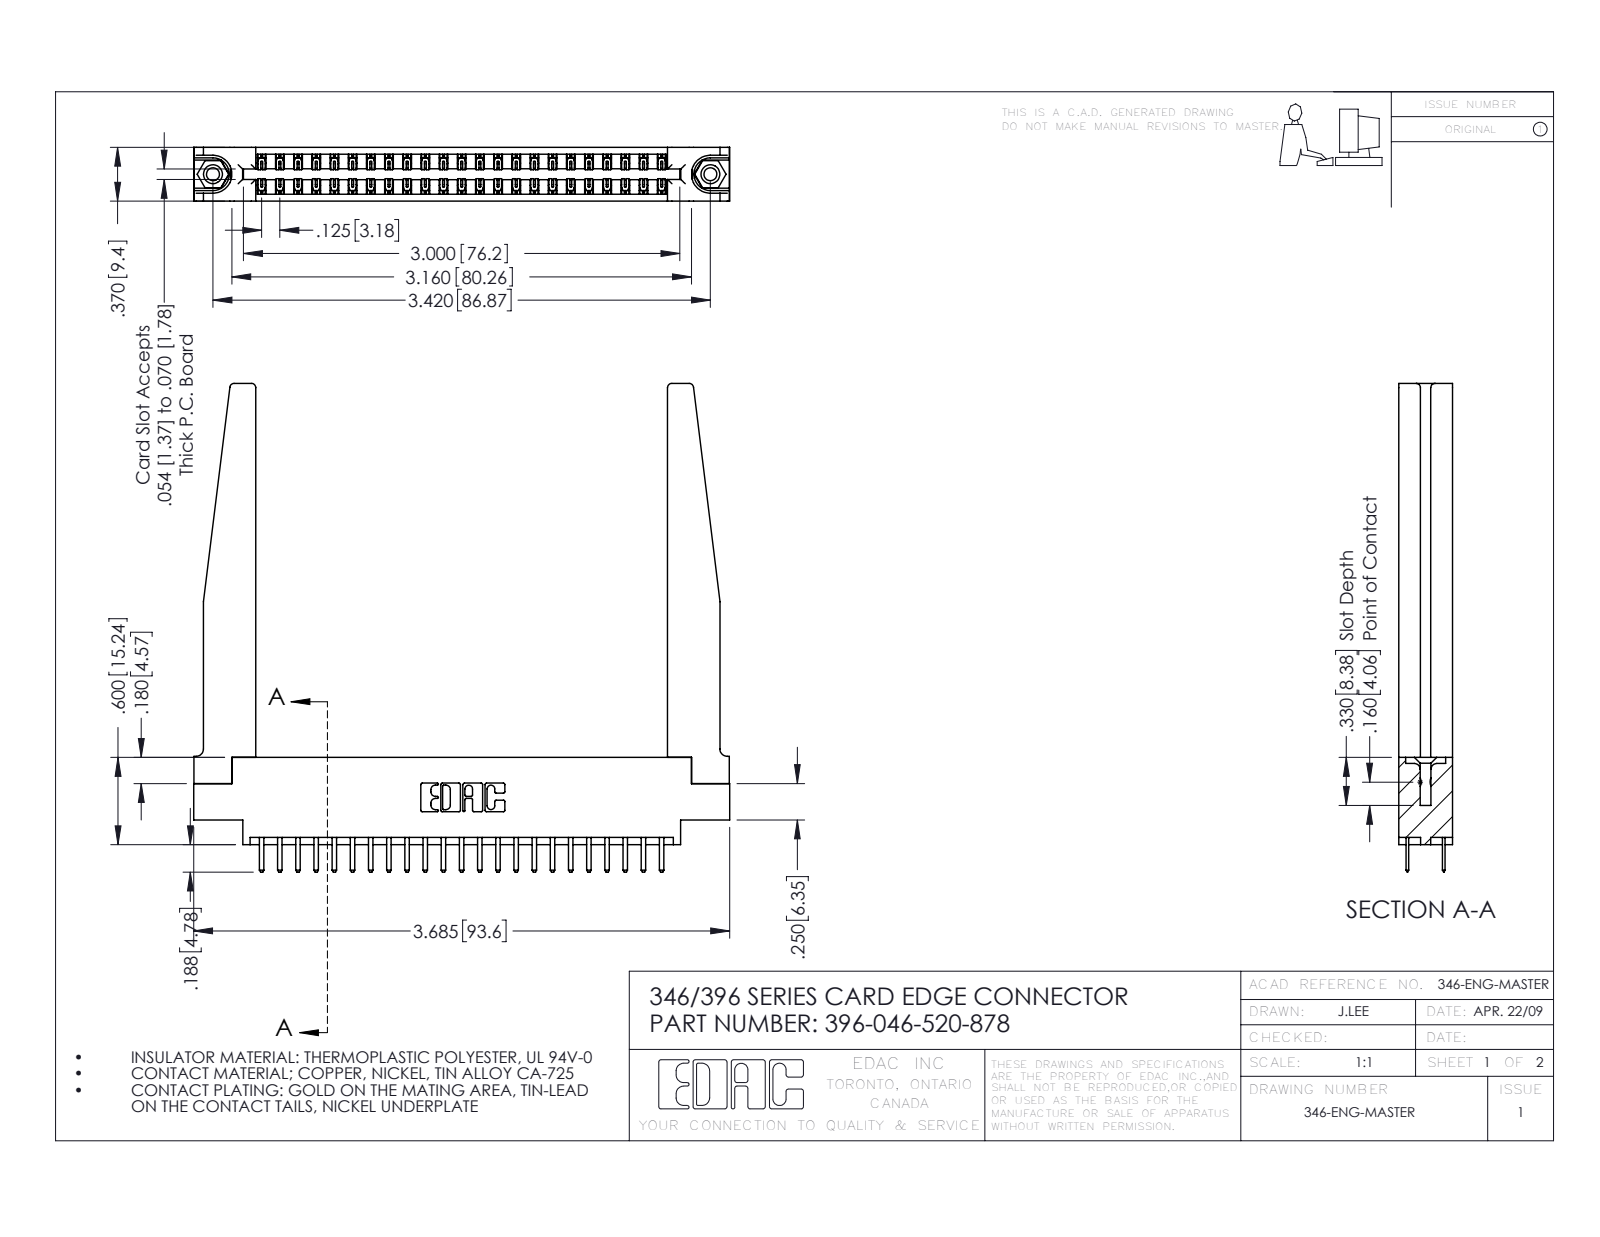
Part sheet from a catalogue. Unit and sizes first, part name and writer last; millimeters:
Units: millimetres
Overall size (bounding box): 93.6 × 85.3 × 9.4
Round holes (diameter × count): ⌀2.3 ×2, ⌀3.2 ×2, ⌀4 ×2, ⌀1.6 ×1
Round bosses / shafts (diameter × count): ⌀3.9 ×2
Partial cylindrical surfaces — rounded edges, fillets, slot ends (radius × count): R0.2 ×69, R0.3 ×50, R0.3 ×22, R0.8 ×8, R0.2 ×6, R0.8 ×6, R0.7 ×3, R0.4 ×2
Main face-to-face distances: 9.4, 1.2, 8.2, 1.8, 3.8, 3.8, 6.4, 7.6, 0.6, 7
Hole centre spacings: 6.2, 81.6, 86.9
Volume: 15 700 mm³ · Surface area: 18 470 mm²
Bodies: 51 solids, 2936 faces (1924 planar, 960 cylindrical, 52 other)
Part name (STEP PRODUCT): 346 Part_0.170 Offset - 0.156 Dia-TH; 346-220-078_345-220-078; 396-046-520-878; 345-292-001_345-293-120 (+1 more)
STEP written by: SolidWorks 2016 (CONFIG_CONTROL_DESIGN)
